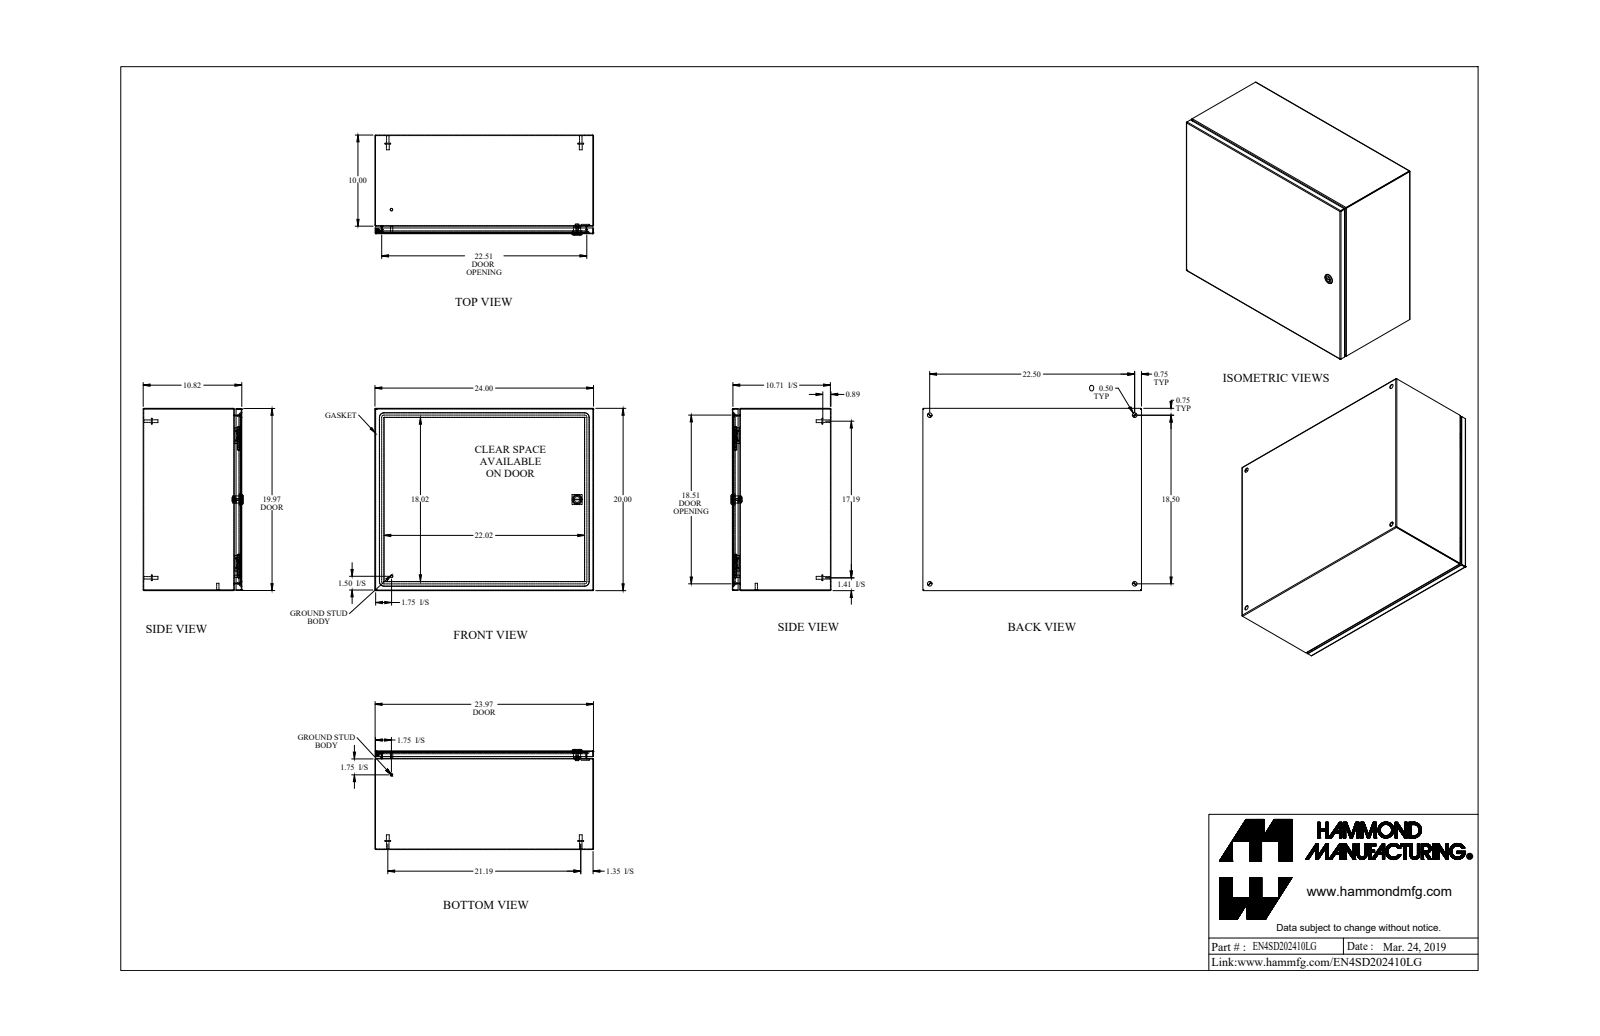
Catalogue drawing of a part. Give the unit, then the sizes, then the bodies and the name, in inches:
Units: inches
Overall size (bounding box): 24 × 20 × 10.982
Round holes (diameter × count): ⌀0.5 ×4, ⌀0.172 ×1, ⌀0.232 ×1, ⌀0.24 ×1, ⌀0.242 ×1, ⌀0.625 ×1, ⌀0.785 ×1
Round bosses / shafts (diameter × count): ⌀0.625 ×4, ⌀0.313 ×4, ⌀0.27 ×4, ⌀0.281 ×2, ⌀0.25 ×2, ⌀1.1 ×1, ⌀0.525 ×1, ⌀0.455 ×1
Partial cylindrical surfaces — rounded edges, fillets, slot ends (radius × count): R0.029 ×21, R0.086 ×21, R0.25 ×16, R19 ×8, R0.006 ×4, R0.062 ×4, R0.499 ×4, R0.125 ×2
Main face-to-face distances: 0.057, 10.765, 10.708, 10.822, 19.943, 23.943, 19.886, 20, 23.886, 24
Hole centre spacings: 18.5, 22.5, 23.351, 29.129, 9.31, 9.311
Volume: 123.2 in³ · Surface area: 4 216 in²
Bodies: 21 solids, 634 faces (285 planar, 213 cylindrical, 136 other)
Part name (STEP PRODUCT): EN4SD202410LG_Default
STEP written by: SolidWorks 2019 (CONFIG_CONTROL_DESIGN)
